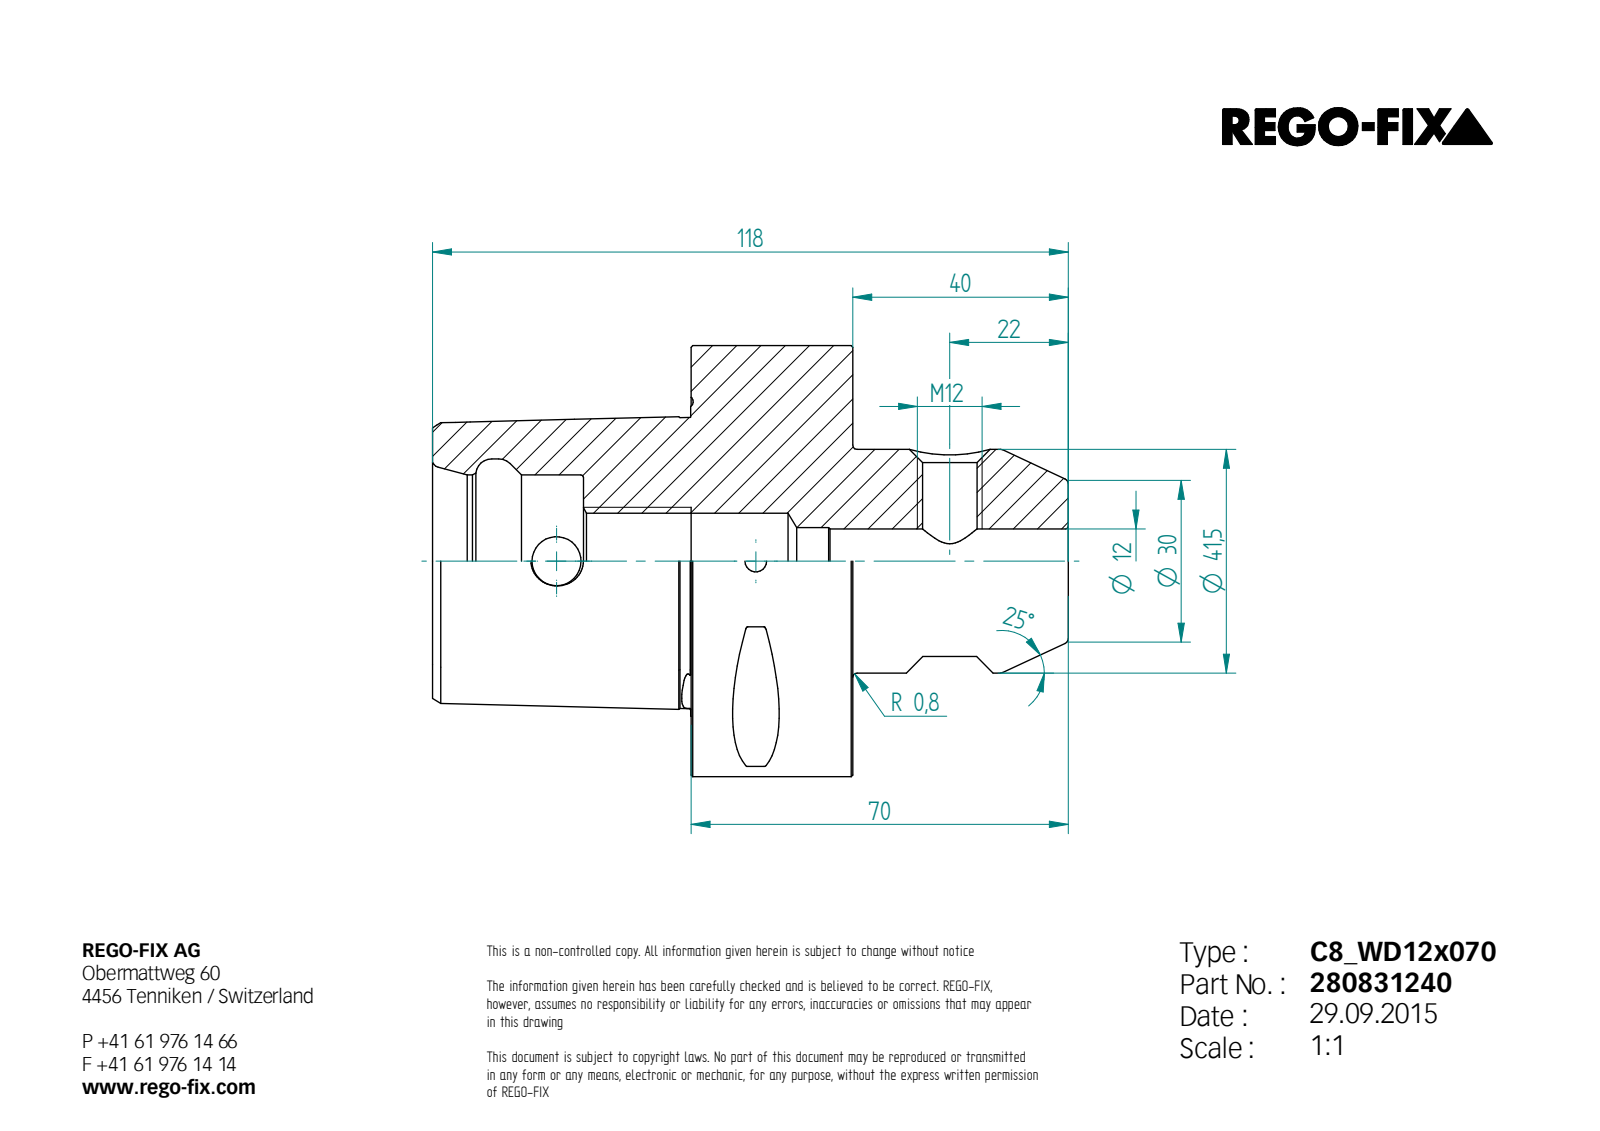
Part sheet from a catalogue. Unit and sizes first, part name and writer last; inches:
Units: inches
Overall size (bounding box): 4.646 × 3.15 × 3.15
Round holes (diameter × count): ⌀0.157 ×1, ⌀0.358 ×1, ⌀0.398 ×1, ⌀0.472 ×1, ⌀0.492 ×1, ⌀0.702 ×1, ⌀1.26 ×1, ⌀1.496 ×1
Round bosses / shafts (diameter × count): ⌀3.15 ×1, ⌀1.634 ×1
Partial cylindrical surfaces — rounded edges, fillets, slot ends (radius × count): R0.02 ×8
Main face-to-face distances: 1.181, 1.89, 3.071, 4.646, 2.756, 1.575, 1.281, 1.102, 0.787, 1.969
Hole centre spacings: 1.457
Volume: 15.95 in³ · Surface area: 58.64 in²
Bodies: 1 solid, 104 faces (23 planar, 21 cylindrical, 60 other)
STEP written by: Unknown (AUTOMOTIVE_DESIGN)
